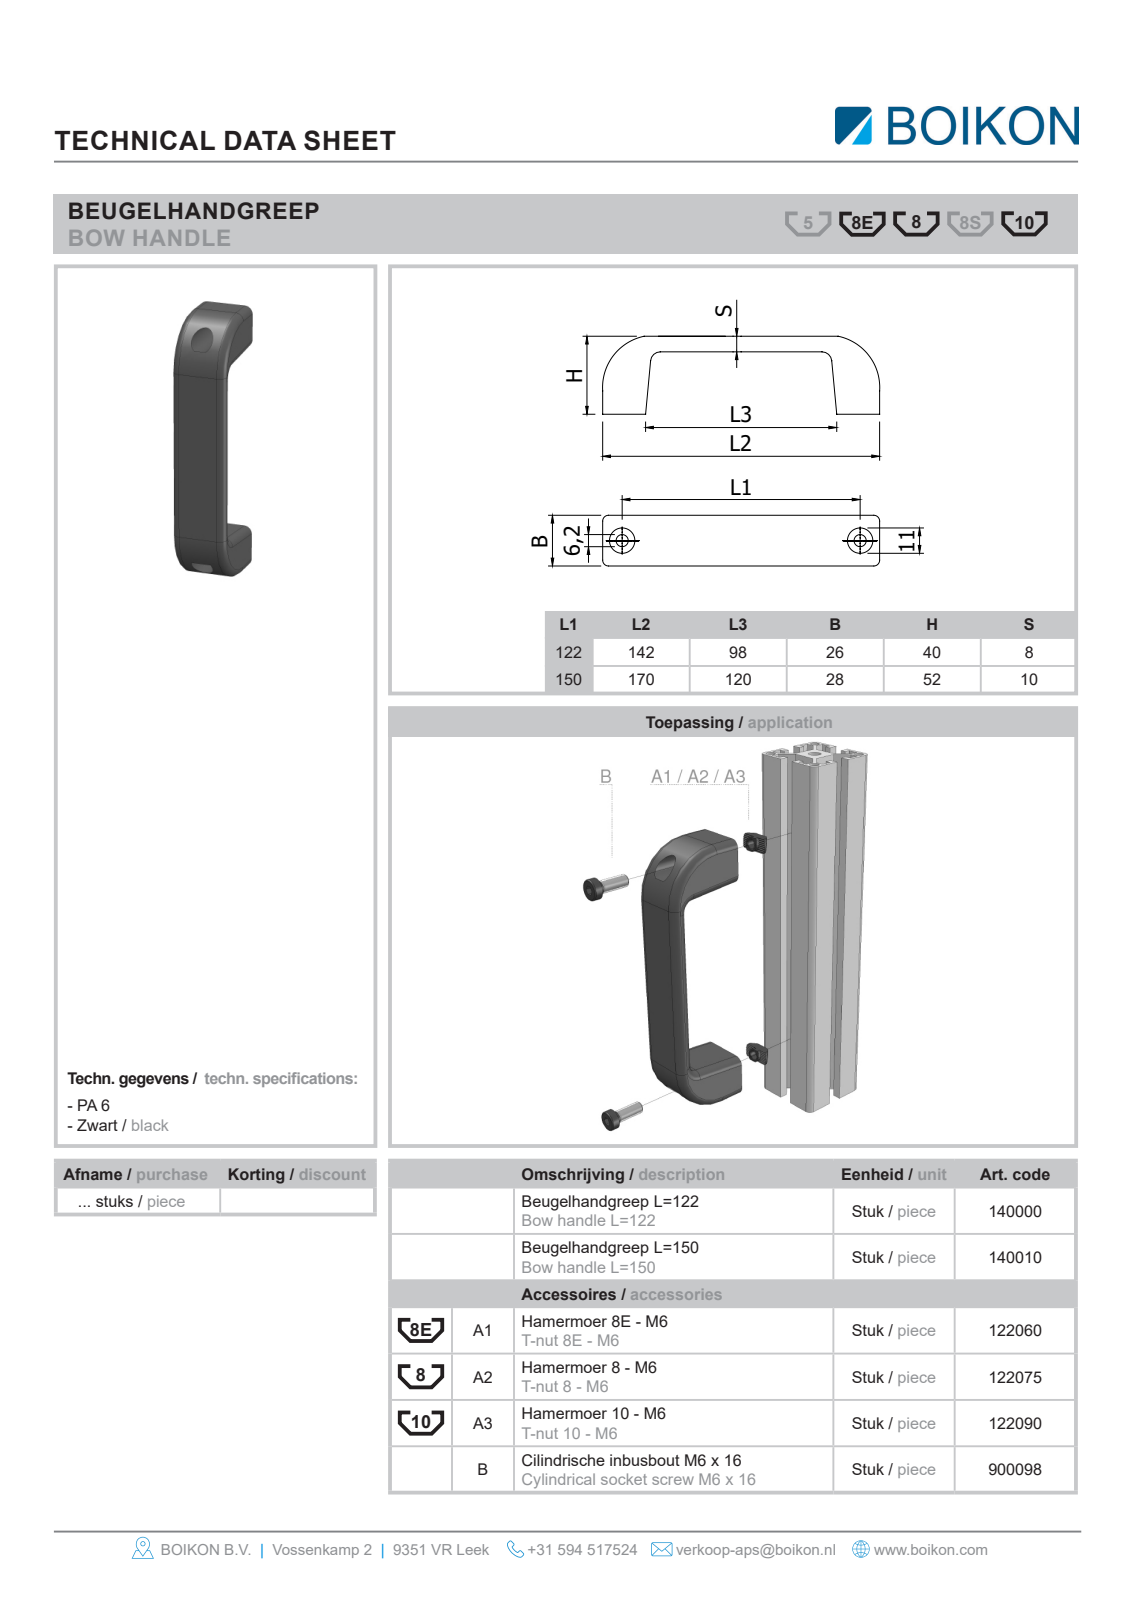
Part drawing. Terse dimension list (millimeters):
name: Root; 140010Beugelgreep, L = 150BOIKON0
written by: HiCAD 2013 1802.4 Build 509 (AUTOMOTIVE_DESIGN)
unit: mm
bodies: 1 solid, 38 faces (10 planar, 18 cylindrical, 10 other)
size: 170 × 52 × 28
volume: 89 248 mm³; area: 18 937 mm²
holes: 2× ⌀6.2
rounds: 12× R4, 2× R5, 2× R39
face distances: 10, 28, 52, 42, 170
hole spacings: 150
